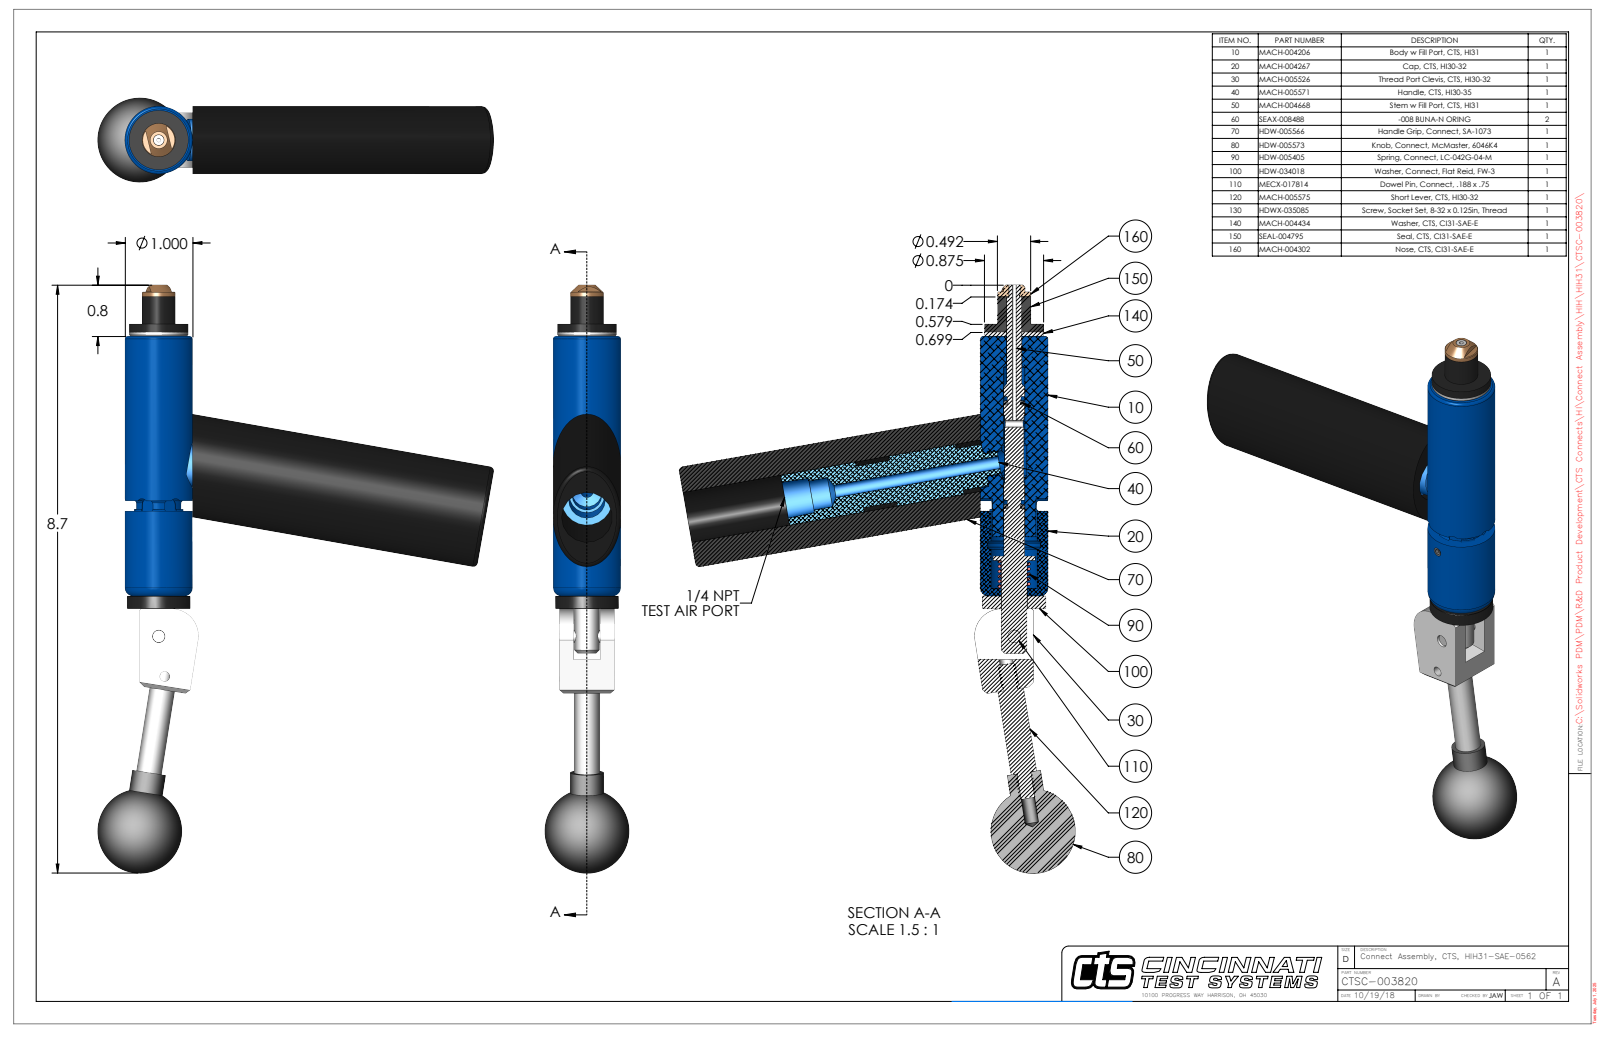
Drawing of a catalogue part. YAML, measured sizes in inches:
part_name: "CTSC-003820"
step_written_by: "SolidWorks 2023 (AUTOMOTIVE_DESIGN)"
units: inches
bodies: {solids: 10, faces: 310, planar: 117, cylindrical: 124, other: 69}
overall_size: [8.692, 5.856, 1.25]
volume: 9.35
surface_area: 76.7
round_holes:
  - {diameter: 0.201, count: 2}
  - {diameter: 0.063, count: 1}
  - {diameter: 0.109, count: 1}
  - {diameter: 0.136, count: 1}
  - {diameter: 0.15, count: 1}
  - {diameter: 0.159, count: 1}
  - {diameter: 0.187, count: 1}
  - {diameter: 0.189, count: 1}
  - {diameter: 0.218, count: 1}
  - {diameter: 0.228, count: 1}
  - {diameter: 0.229, count: 1}
  - {diameter: 0.385, count: 1}
round_bosses_or_shafts:
  - {diameter: 1, count: 1}
  - {diameter: 0.936, count: 1}
  - {diameter: 0.875, count: 1}
  - {diameter: 0.875, count: 1}
  - {diameter: 0.75, count: 1}
  - {diameter: 0.62, count: 1}
  - {diameter: 0.5, count: 1}
  - {diameter: 0.492, count: 1}
partial_cylinders:
  - {radius: 0.093, count: 6}
  - {radius: 0.029, count: 2}
  - {radius: 0.059, count: 1}
  - {radius: 0.325, count: 1}
  - {radius: 0.375, count: 1}
  - {radius: 0.4, count: 1}
  - {radius: 0.464, count: 1}
face_to_face_distances: [0.21, 0.602, 0.06, 3.896, 3.835, 0.812, 4.083, 4.023, 0.187, 0.391]
hole_center_spacings: [0.599, 1.658, 2.252]
